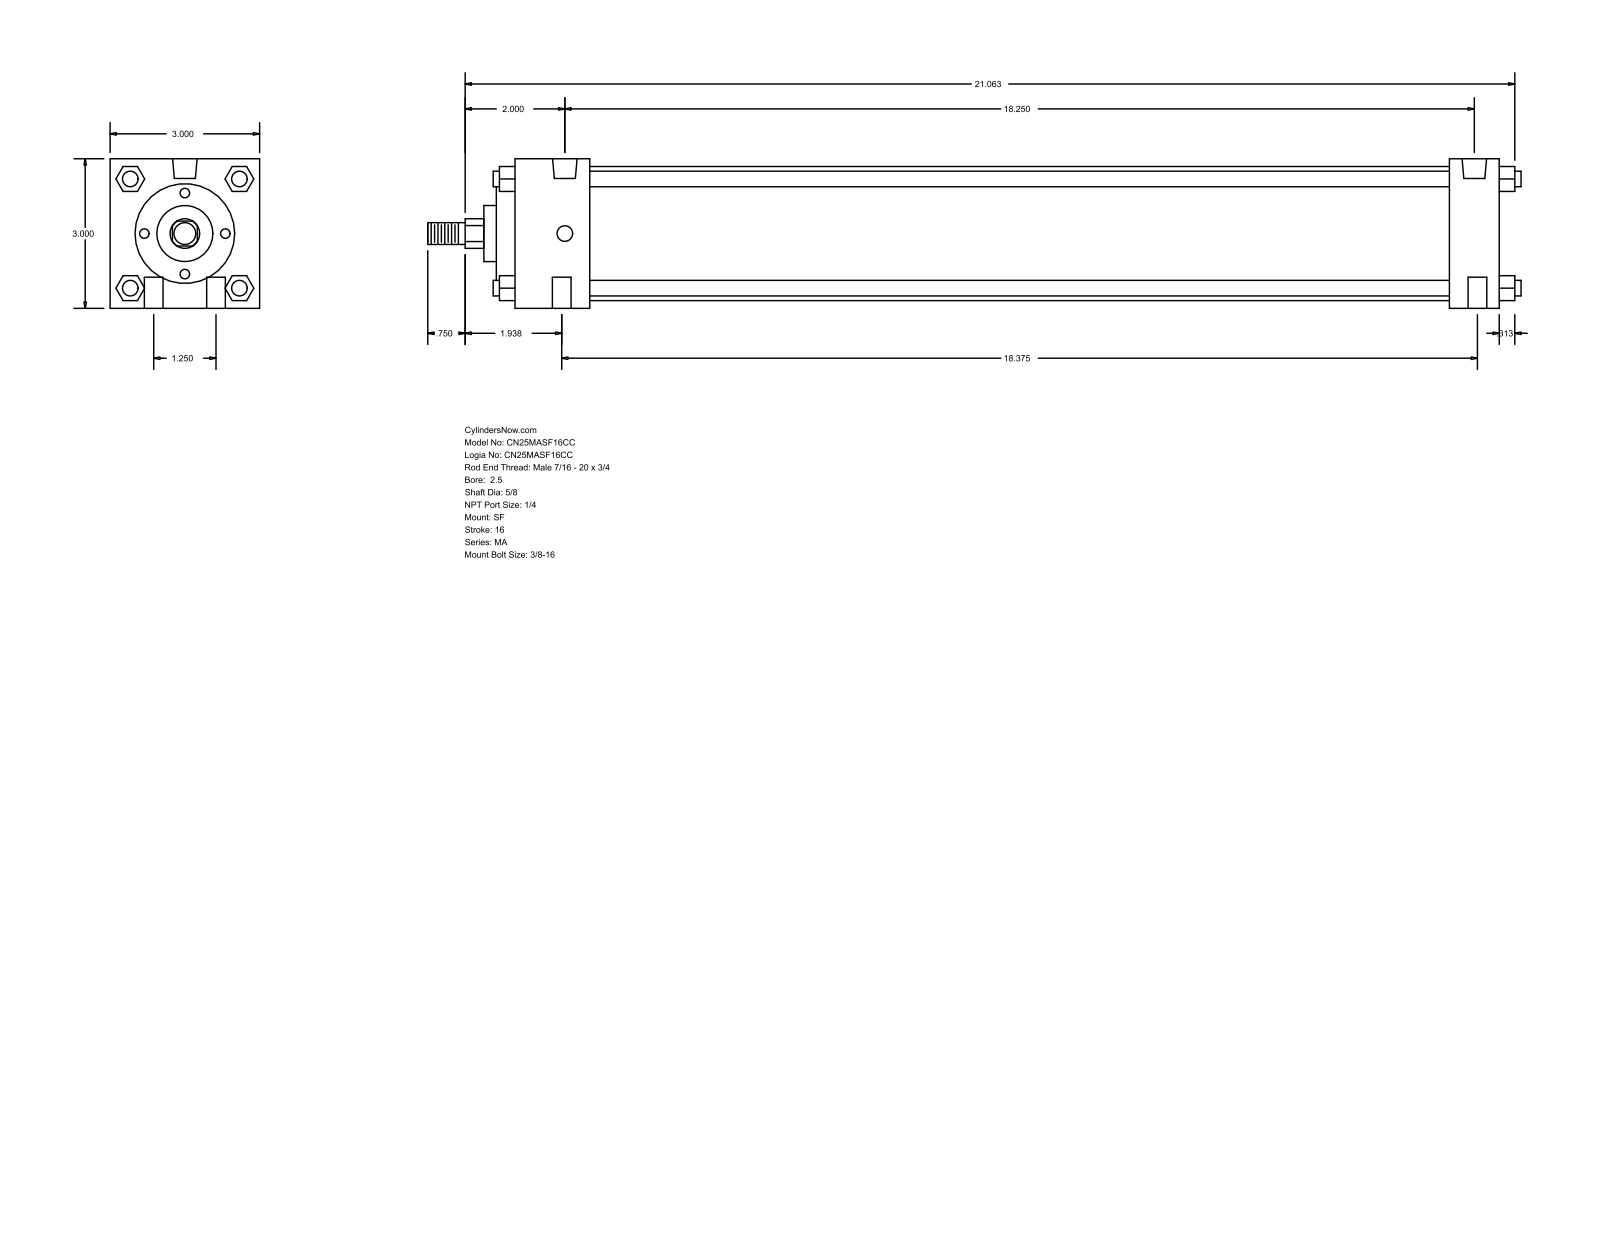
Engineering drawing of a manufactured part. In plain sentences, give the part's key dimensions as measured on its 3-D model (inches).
The part is named "MA_SF__0250_0.625". Its 3-D file was written by "GSSL Pune (CONFIG_CONTROL_DESIGN)". It is 0 solids with 126 faces: 95 planar, 31 cylindrical and 0 other. Overall it measures 21.937 by 3 by 3 inches. Round holes: 4 of diameter 0.375, 2 of diameter 0.313, 2 of diameter 0.492. Round bosses or shafts: 4 of diameter 0.313, 1 of diameter 2.69, 1 of diameter 2, 1 of diameter 1.125, 1 of diameter 0.625, 1 of diameter 0.437. Partial cylindrical surfaces (rounded edges, fillets, slot ends): 1 of radius 0.297. The main face-to-face distances are 3, 19.75, 1, 18.75, 1.5, 17.25, 18.25, 0.5, 0.375, 1.875. The hole center spacings are 0.628, 18.323, 1.25, 18.25, 18.375, 18.418.
